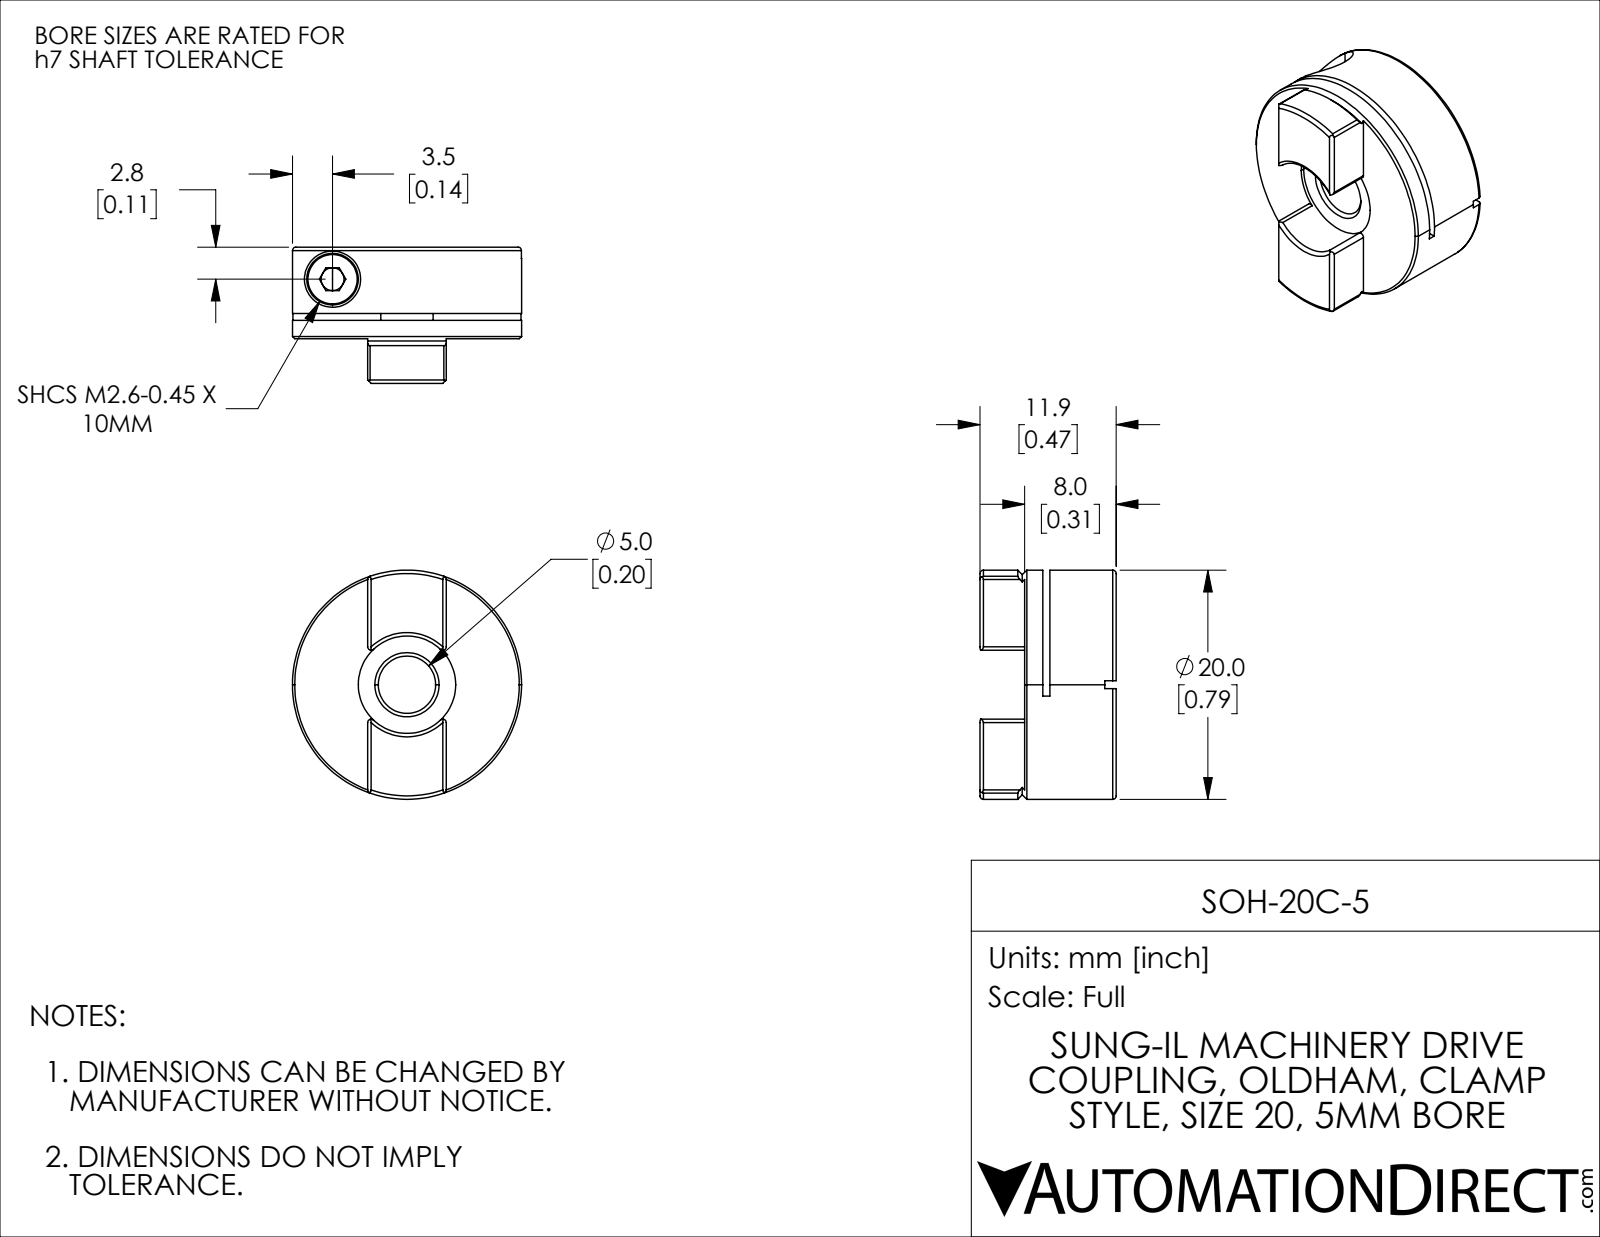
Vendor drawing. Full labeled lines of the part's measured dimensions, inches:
Part name (STEP PRODUCT): SOH-20C-5
STEP written by: SolidWorks 2021 (CONFIG_CONTROL_DESIGN)
Units: inches
Bodies: 2 solids, 99 faces (40 planar, 33 cylindrical, 26 other)
Overall size (bounding box): 0.787 × 0.787 × 0.469
Volume: 0.15 in³ · Surface area: 3.23 in²
Round holes (diameter × count): ⌀0.079 ×1, ⌀0.081 ×1, ⌀0.11 ×1, ⌀0.193 ×1, ⌀0.197 ×1, ⌀0.335 ×1
Round bosses / shafts (diameter × count): ⌀0.787 ×1, ⌀0.177 ×1, ⌀0.102 ×1
Partial cylindrical surfaces — rounded edges, fillets, slot ends (radius × count): R0.012 ×8, R0.886 ×1
Main face-to-face distances: 0.315, 0.228, 0.252, 0.063, 0.024, 0.087, 0.154, 0.469, 0.24, 0.217
